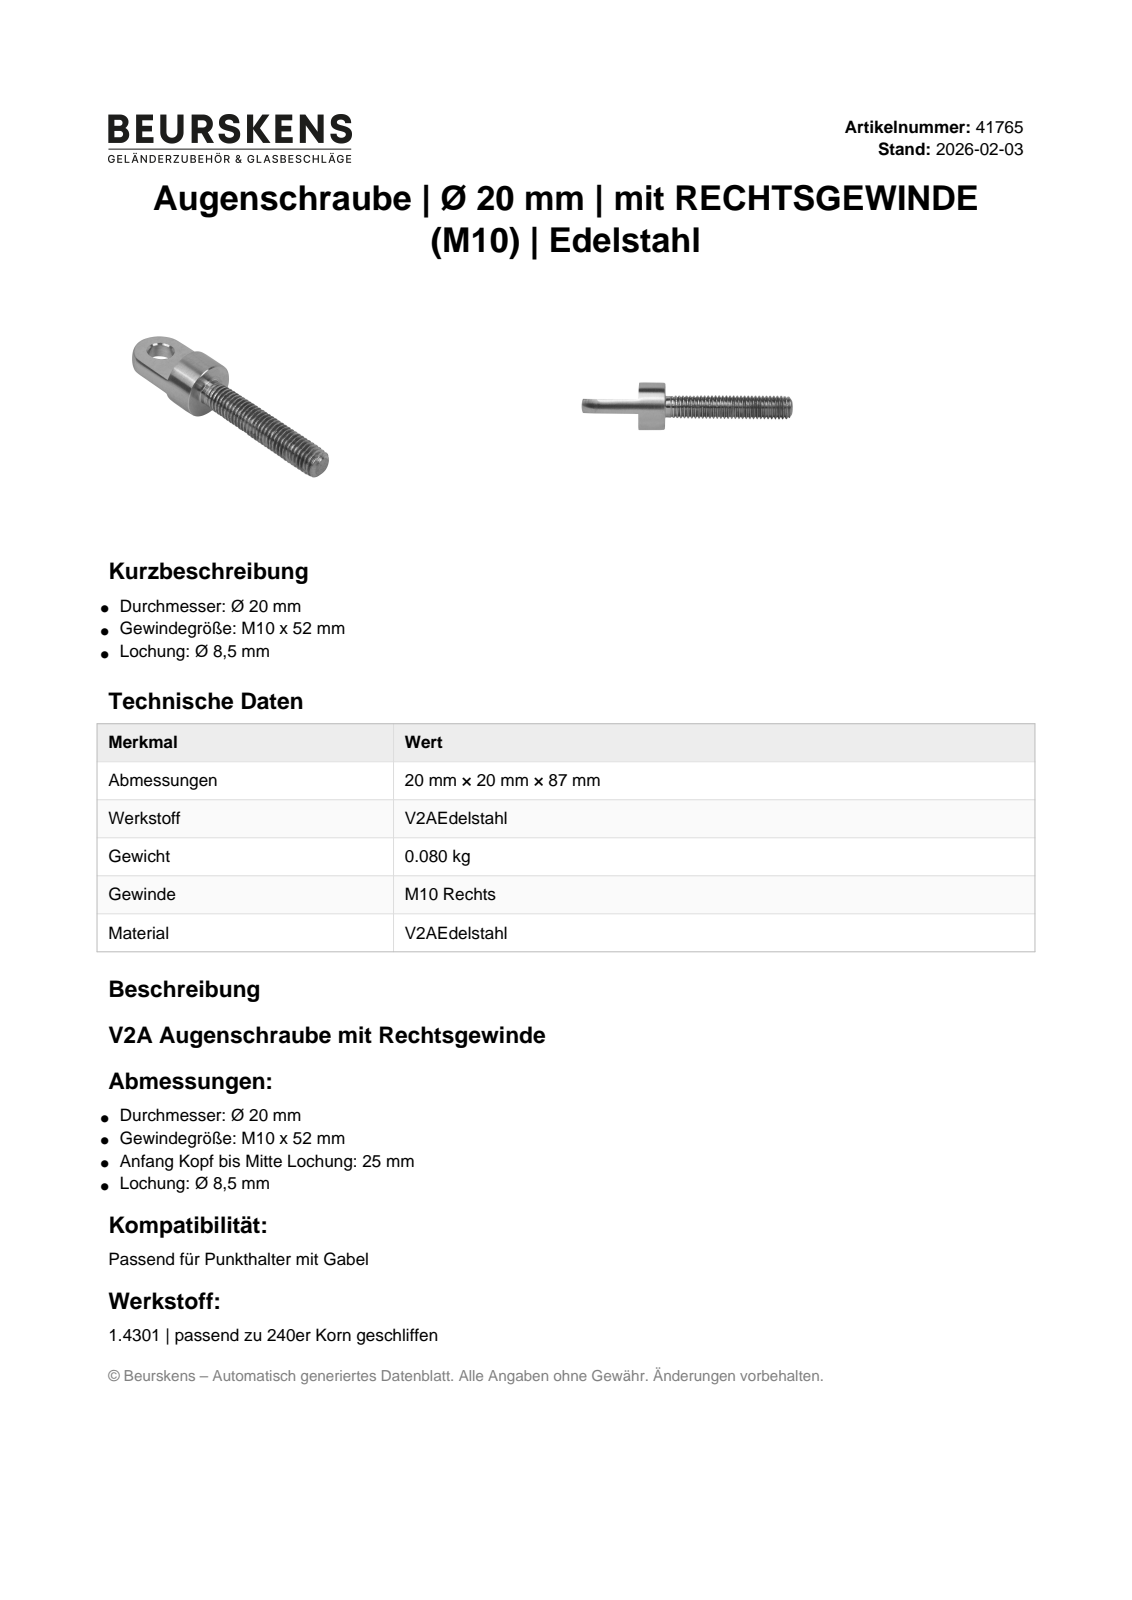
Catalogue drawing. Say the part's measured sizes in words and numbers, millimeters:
The part is named "41765". Its 3-D file was written by "Autodesk Inventor 2022 (AUTOMOTIVE_DESIGN)". It is 1 solid with 12 faces: 6 planar, 3 cylindrical and 3 other. Overall it measures 85 by 20 by 20 millimeters. Its volume is 9 525 cubic millimeters and its surface area 3 937 square millimeters. Round holes: 1 of diameter 8.5. Round bosses or shafts: 1 of diameter 20, 1 of diameter 10. The main face-to-face distances are 6, 11, 52, 63.
